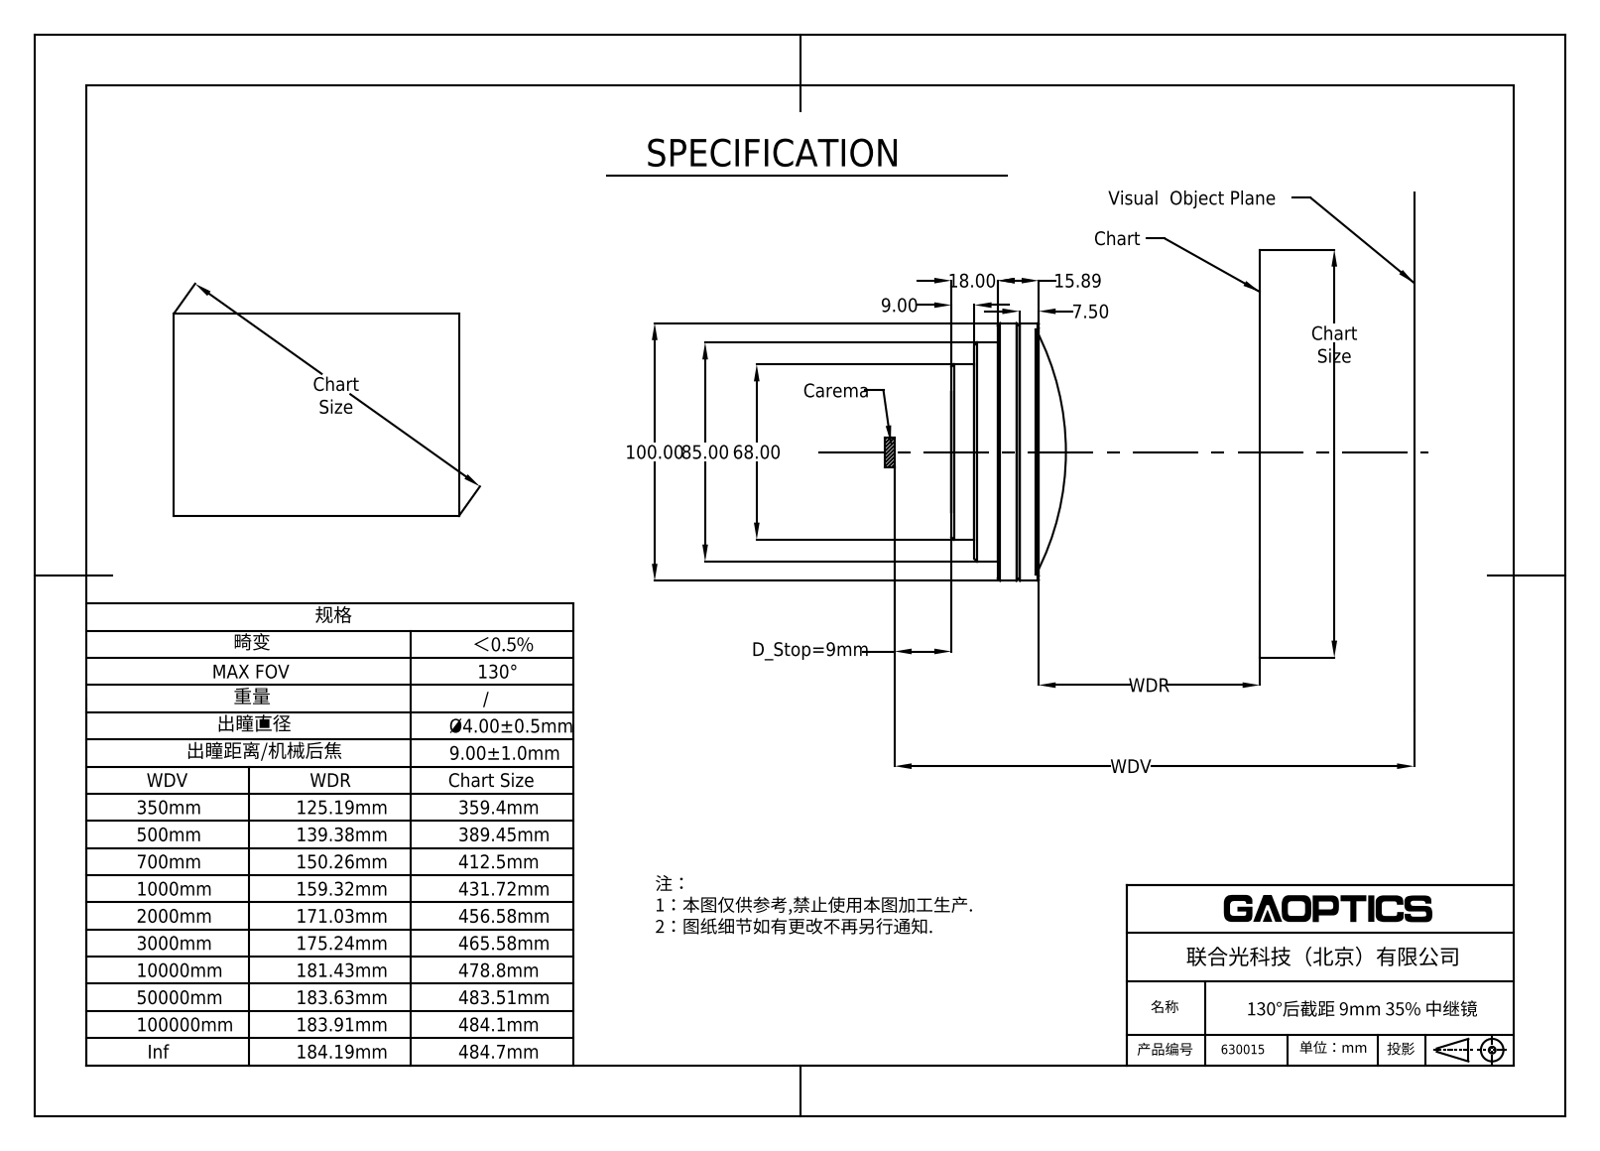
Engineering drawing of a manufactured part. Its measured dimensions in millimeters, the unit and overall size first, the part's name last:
Units: millimetres
Overall size (bounding box): 100 × 100 × 44.47
Round holes (diameter × count): ⌀46.5 ×1, ⌀94.9 ×1
Round bosses / shafts (diameter × count): ⌀100 ×1, ⌀98 ×1, ⌀85 ×1, ⌀68 ×1
Main face-to-face distances: 9, 18, 8.9, 17.9, 33.89, 33.79, 24.89, 15.89, 7.5, 8.39
Volume: 242 304 mm³ · Surface area: 25 636 mm²
Bodies: 1 solid, 37 faces (7 planar, 14 cylindrical, 16 other)
Part name (STEP PRODUCT): 630015
STEP written by: SolidWorks 2020 (CONFIG_CONTROL_DESIGN)
